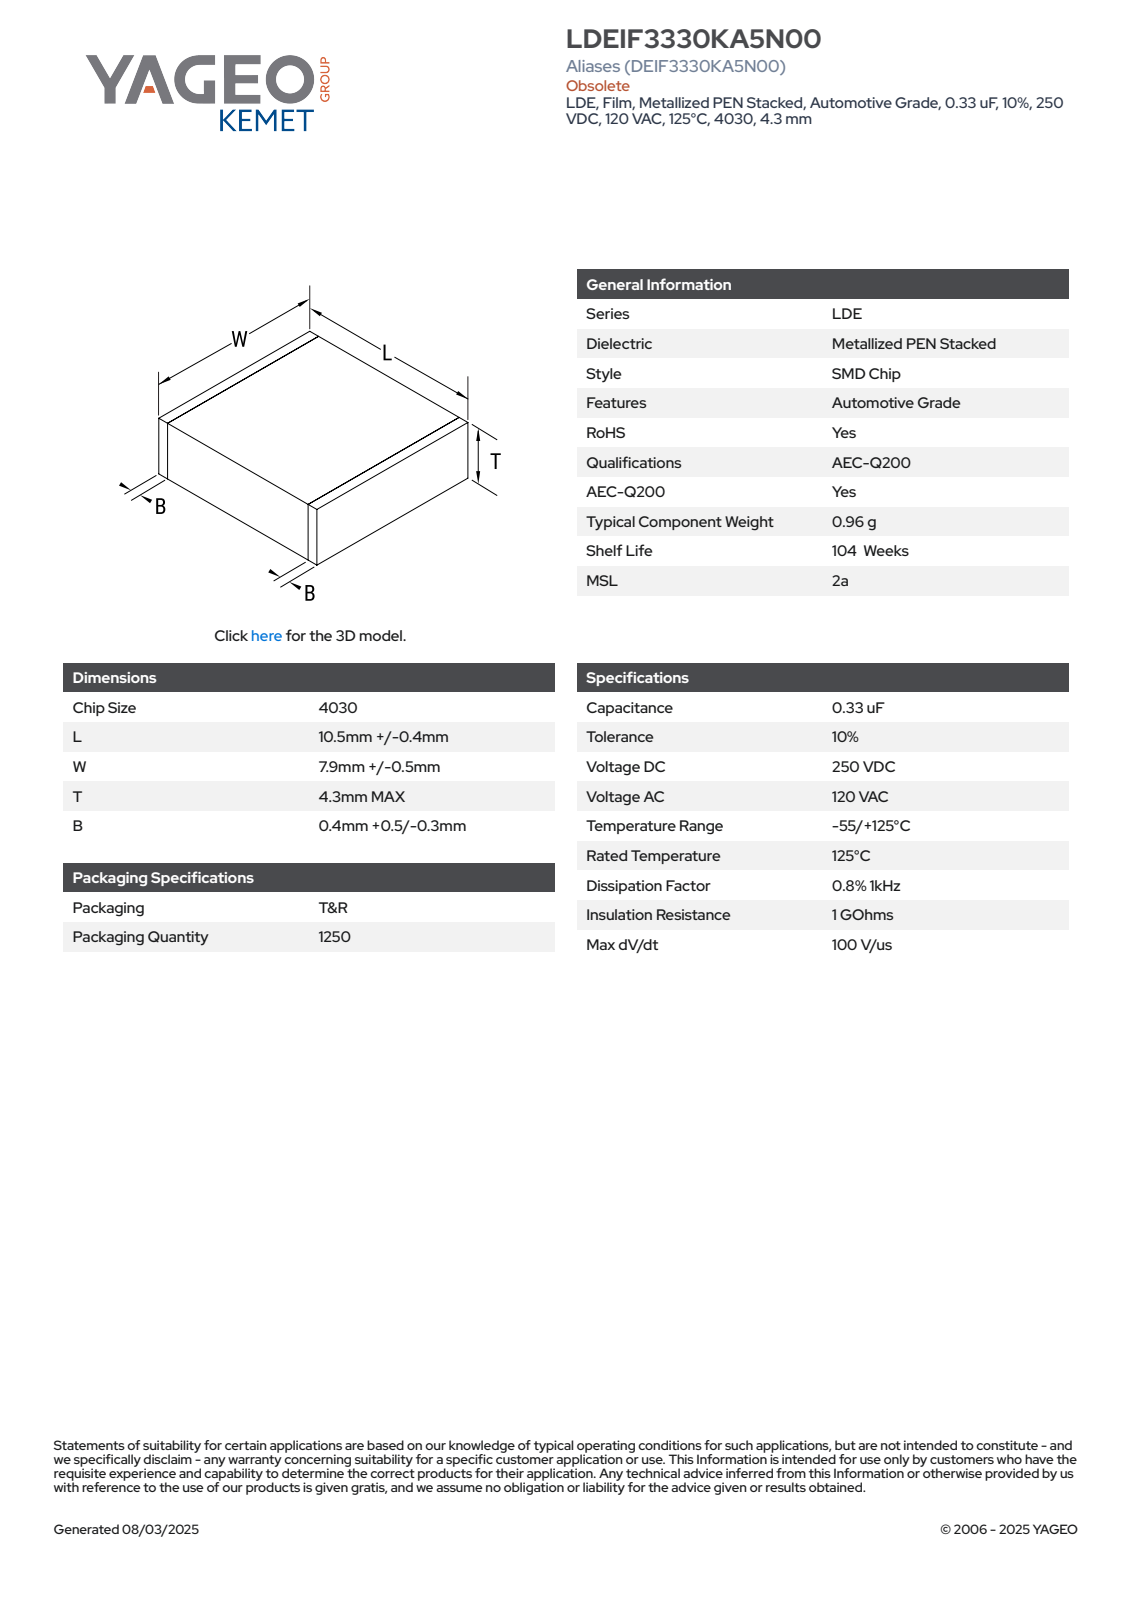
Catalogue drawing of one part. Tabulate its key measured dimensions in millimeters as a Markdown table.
| quantity | value |
| --- | --- |
| part name | CFS_LDELDB_4030_L10.9W8.4T4.3B0.9 |
| STEP written by | SolidWorks 2020 (AUTOMOTIVE_DESIGN) |
| units | millimeters |
| bodies | 4 solids, 73 faces (73 planar, 0 cylindrical, 0 other) |
| overall size | 10.9 × 8.4 × 4.3 |
| volume | 391 mm³ |
| surface area | 354 mm² |
| main face-to-face distances | 4.28, 8.38, 10.9, 4.29, 8.39, 4.3, 8.4, 0.5, 10.4, 9.9 |
